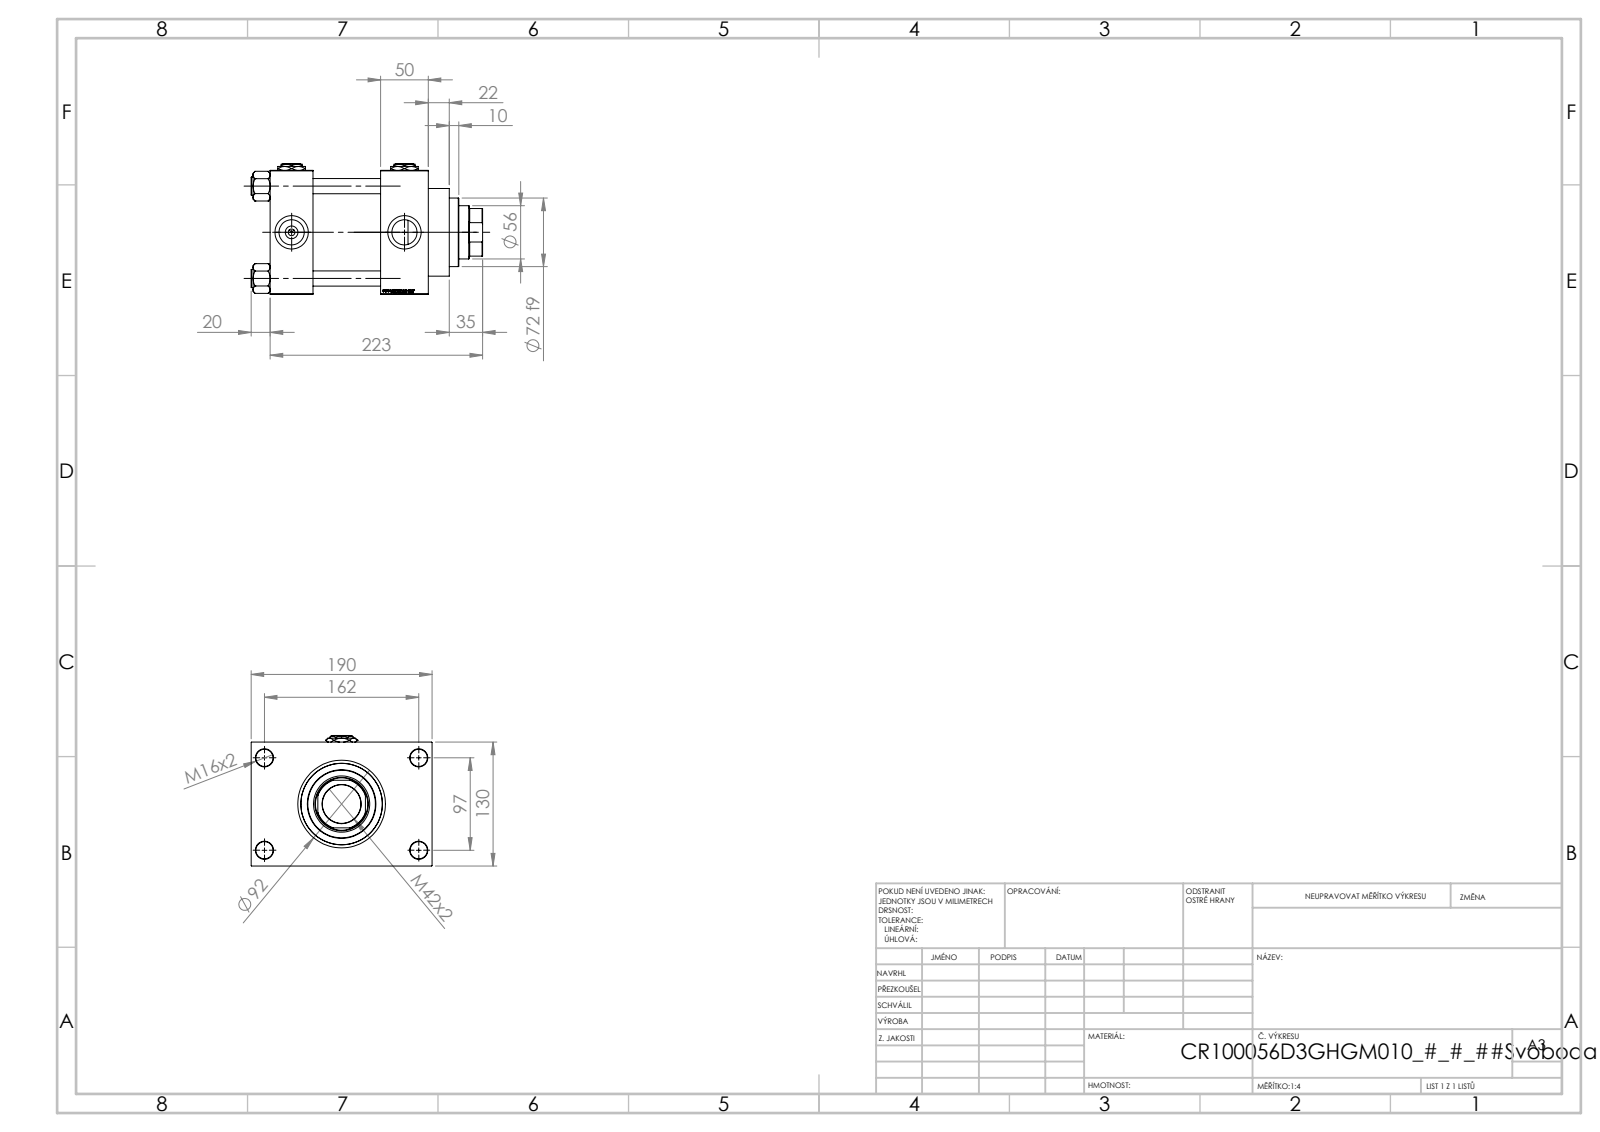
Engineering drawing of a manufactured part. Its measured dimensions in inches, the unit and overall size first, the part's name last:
Units: inches
Overall size (bounding box): 9.567 × 7.48 × 5.394
Round holes (diameter × count): ⌀0.63 ×4, ⌀0.709 ×4, ⌀1.041 ×4, ⌀1.378 ×4, ⌀0.276 ×3, ⌀1.594 ×1, ⌀2.205 ×1, ⌀2.323 ×1, ⌀2.992 ×1, ⌀3.366 ×1, ⌀3.937 ×1
Round bosses / shafts (diameter × count): ⌀0.748 ×4, ⌀4.173 ×1, ⌀3.622 ×1, ⌀2.835 ×1
Partial cylindrical surfaces — rounded edges, fillets, slot ends (radius × count): R1.063 ×1
Main face-to-face distances: 5.118, 4.567, 1.969, 1.772, 2.795, 4.764, 6.535, 1.181, 6.299, 0.787
Hole centre spacings: 1.281, 2.698, 3.717, 3.815, 4.026, 5.096, 6.367, 3.819
Volume: 159.5 in³ · Surface area: 572.4 in²
Bodies: 13 solids, 1252 faces (593 planar, 99 cylindrical, 560 other)
Part name (STEP PRODUCT): V215CR_VCP_D; V215_VC_A; V215CR_D_TYCINKA; V215CR_D_Body (+2 more)
STEP written by: SolidWorks 2019 (CONFIG_CONTROL_DESIGN)
